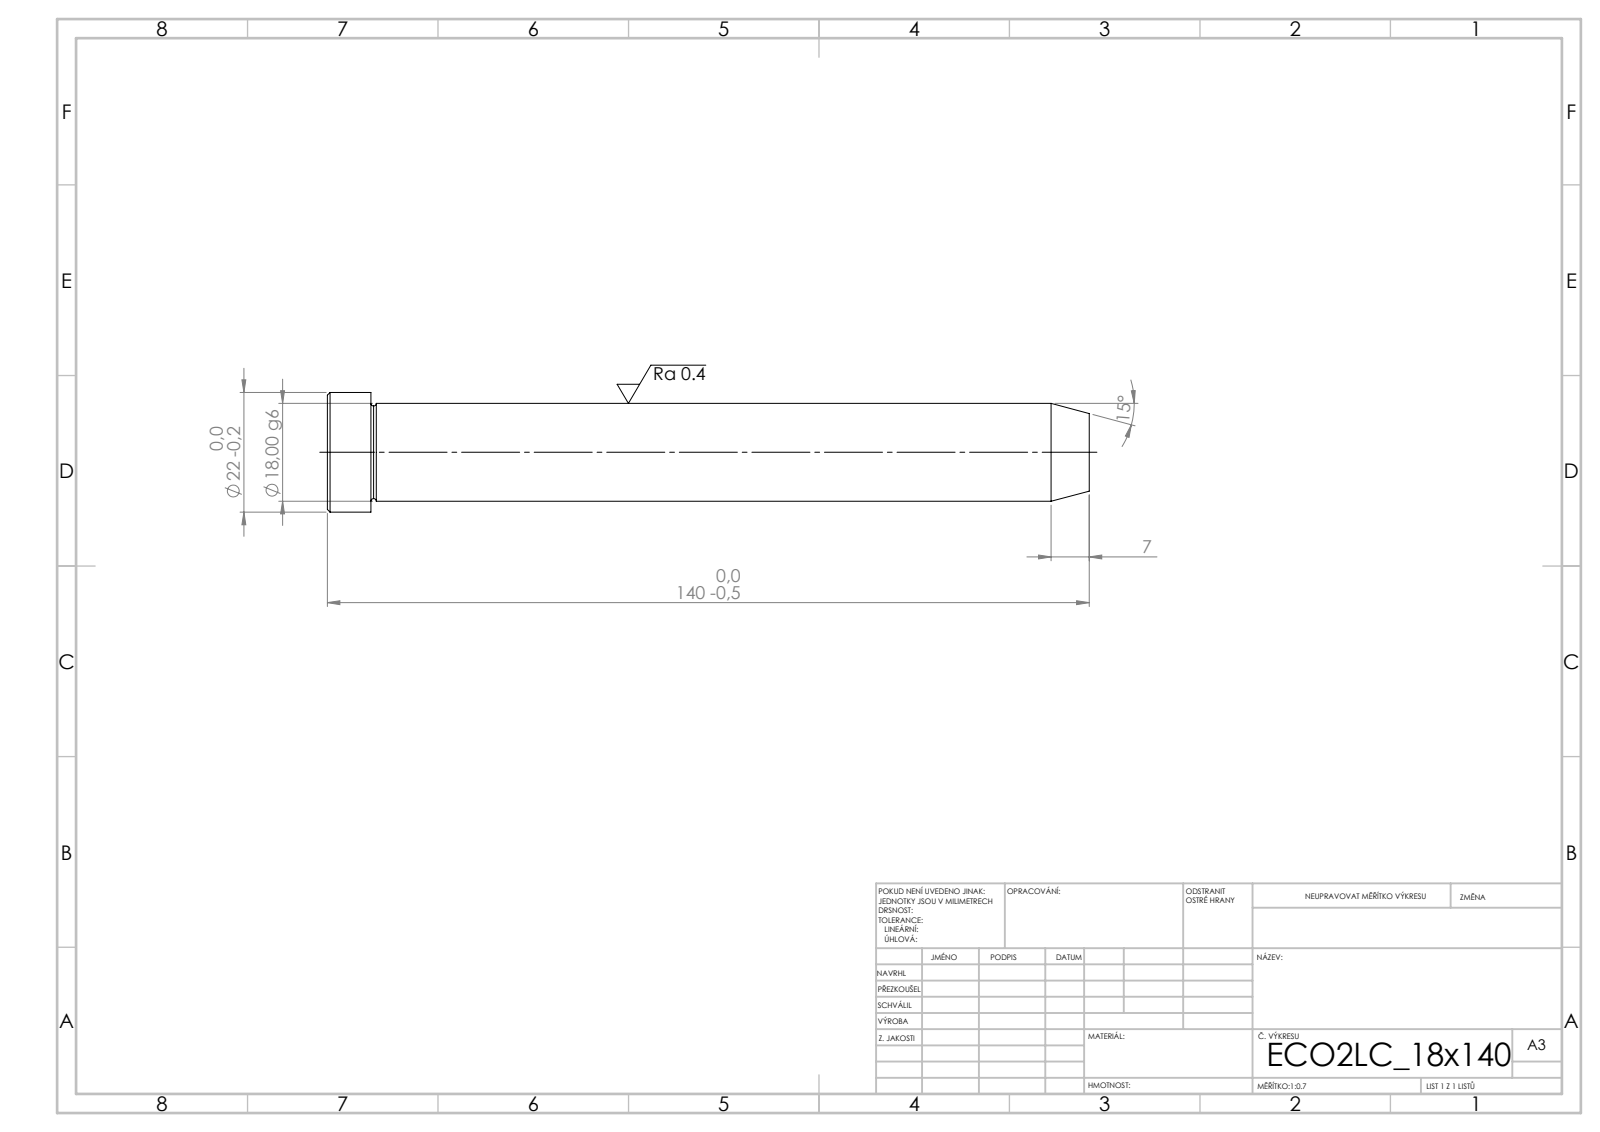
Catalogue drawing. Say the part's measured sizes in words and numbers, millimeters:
Its 3-D file was written by "SolidWorks 2019 (CONFIG_CONTROL_DESIGN)". It is 1 solid with 15 faces: 3 planar, 4 cylindrical and 8 other. Overall it measures 140 by 22 by 22 millimeters. Its volume is 36 255 cubic millimeters and its surface area 8 662 square millimeters. Round bosses or shafts: 1 of diameter 22, 1 of diameter 18. The main face-to-face distances are 140, 132, 8.
